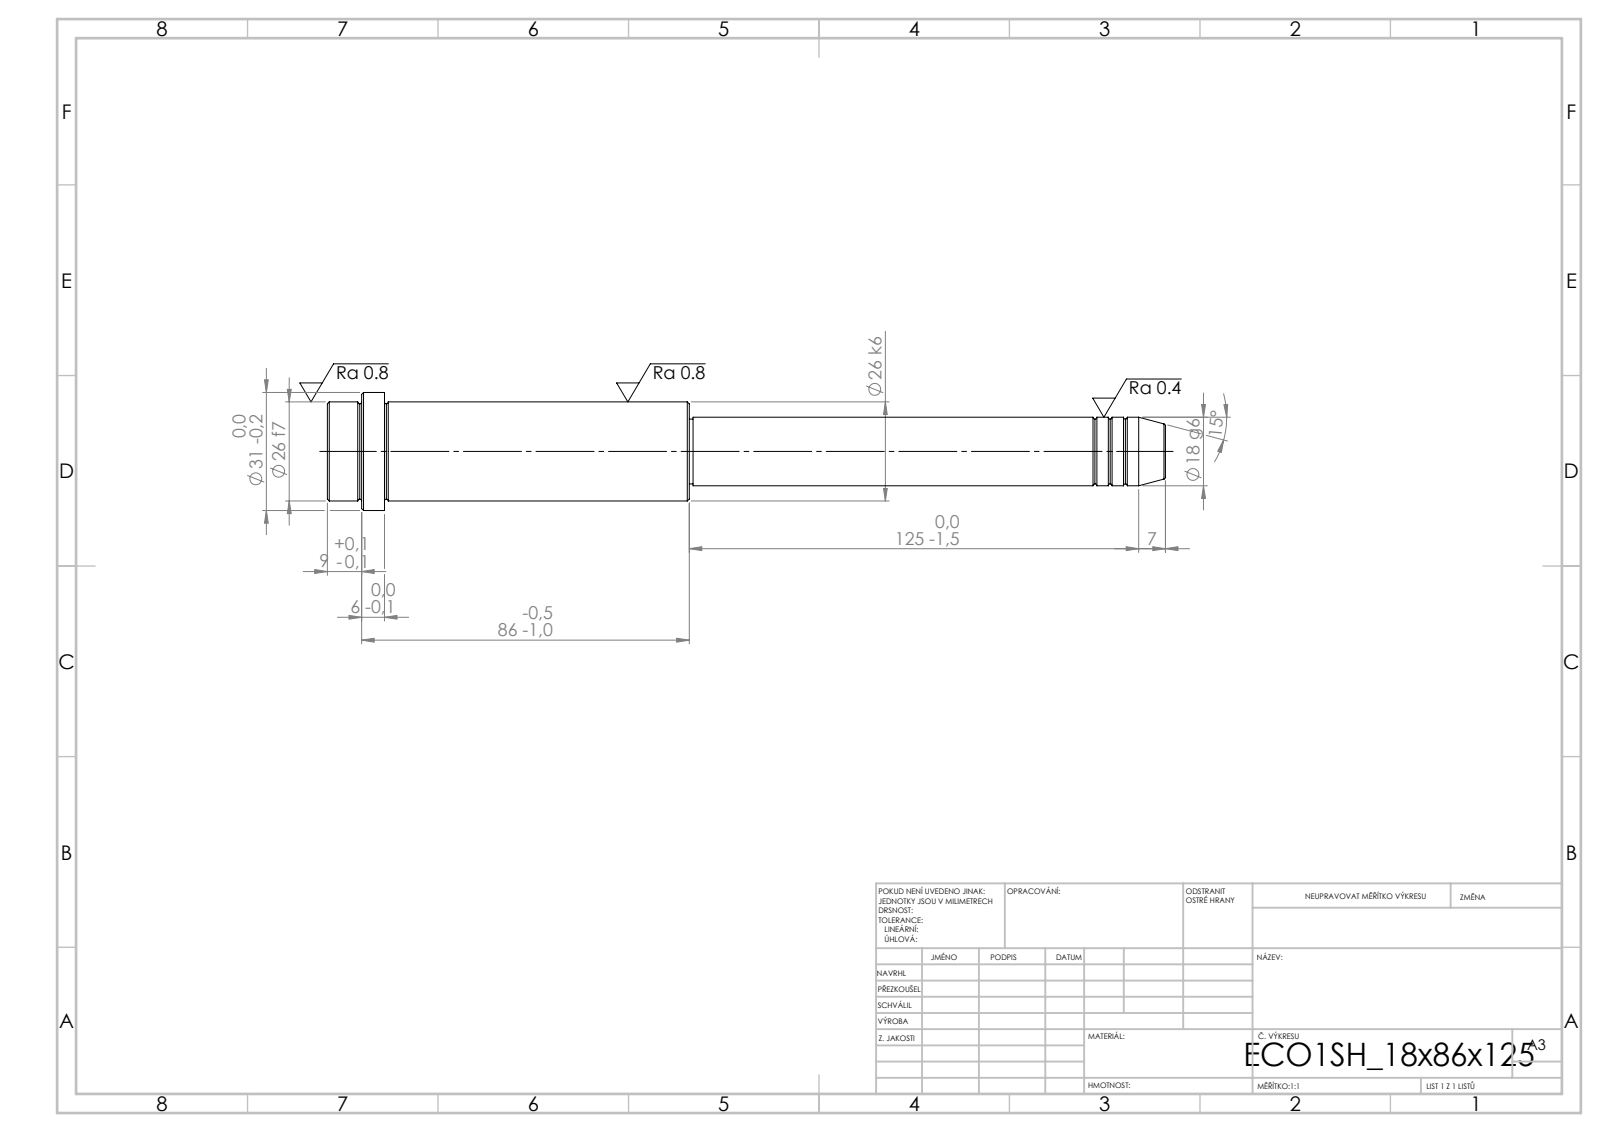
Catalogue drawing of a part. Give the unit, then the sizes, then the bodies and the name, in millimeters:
Units: millimetres
Overall size (bounding box): 220 × 31 × 31
Round bosses / shafts (diameter × count): ⌀31 ×1, ⌀26 ×1, ⌀18 ×1, ⌀17 ×1
Main face-to-face distances: 95, 80, 15, 86, 6, 9, 125, 205, 211, 220
Volume: 83 055 mm³ · Surface area: 16 452 mm²
Bodies: 1 solid, 52 faces (6 planar, 16 cylindrical, 30 other)
STEP written by: SolidWorks 2019 (CONFIG_CONTROL_DESIGN)
